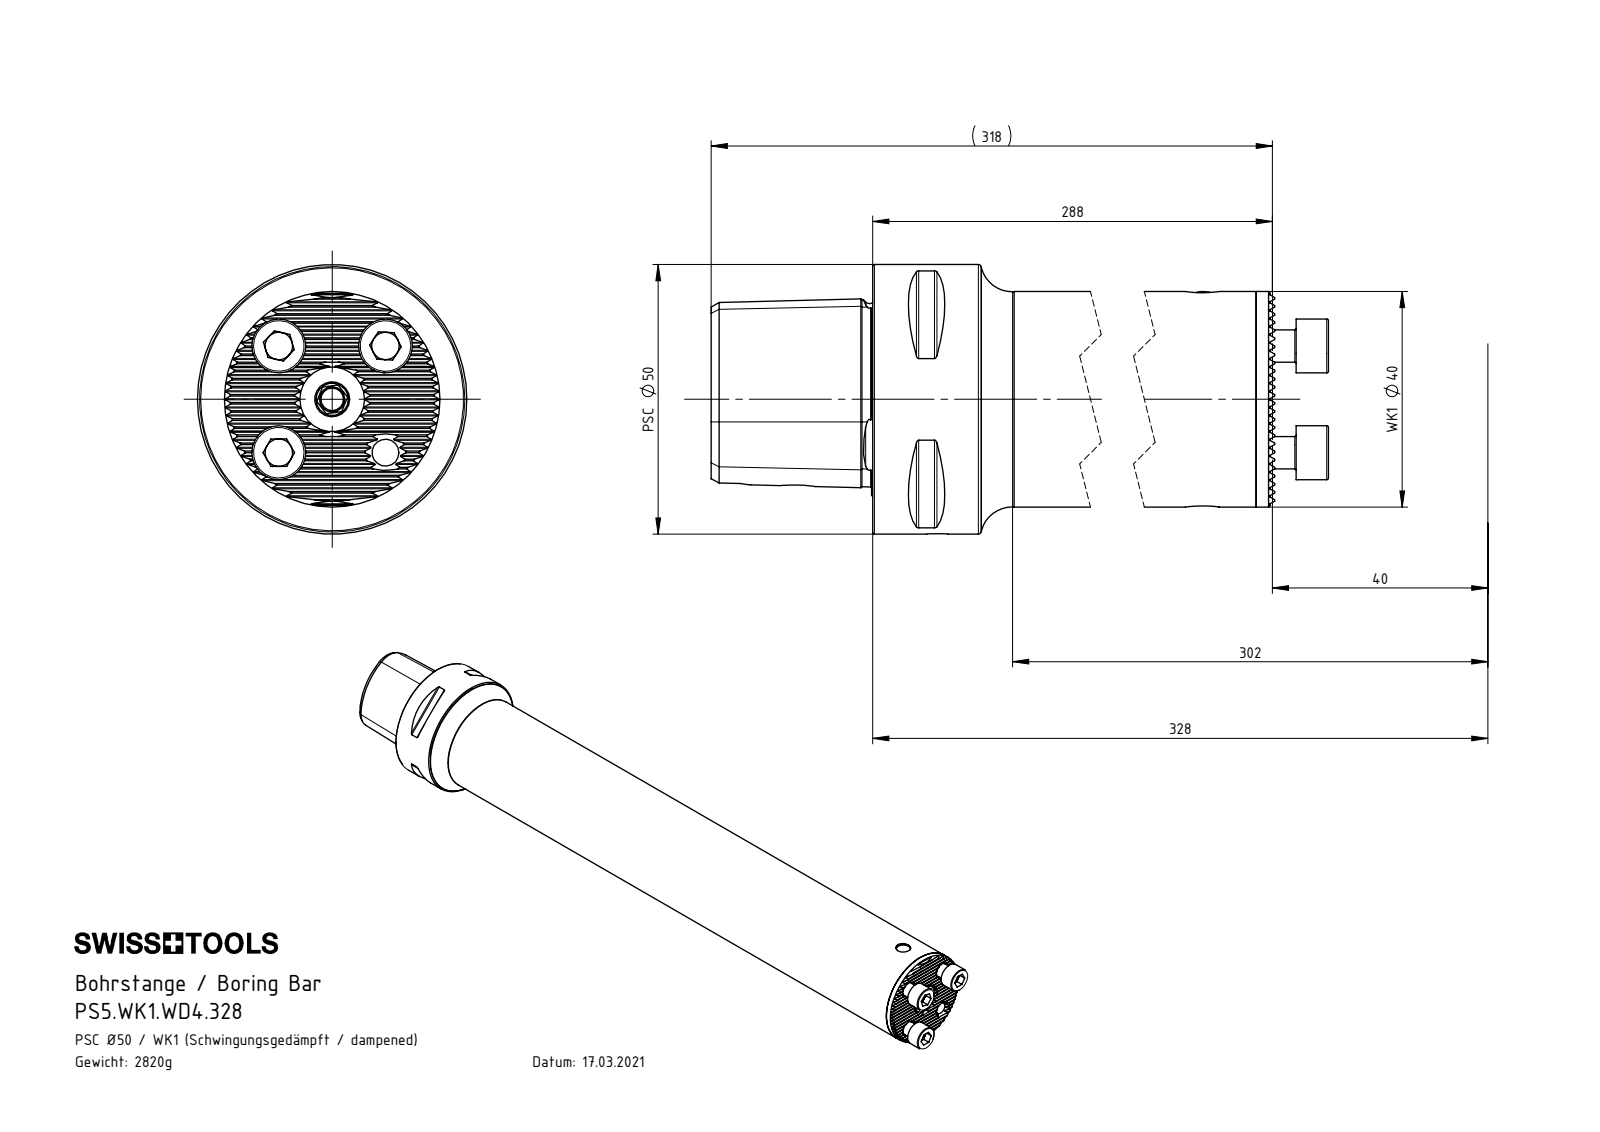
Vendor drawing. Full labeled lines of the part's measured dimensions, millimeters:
Part name (STEP PRODUCT): DIN 3771 - 13x4; WD4-ER1.011.107_A; PS5-WD4.125.285_A_mit Stiftbohrung; DIN 6325_ø6x16-m6_2x6 (+8 more)
STEP written by: SolidWorks 2017 (AUTOMOTIVE_DESIGN)
Units: millimetres
Bodies: 16 solids, 530 faces (266 planar, 120 cylindrical, 144 other)
Overall size (bounding box): 328.4 × 50 × 50
Volume: 364 499 mm³ · Surface area: 108 802 mm²
Round holes (diameter × count): ⌀5 ×4, ⌀6 ×2, ⌀4 ×1, ⌀4.2 ×1, ⌀6.1 ×1, ⌀7 ×1, ⌀7.4 ×1, ⌀8.5 ×1, ⌀12 ×1, ⌀14 ×1, ⌀14.5 ×1, ⌀21 ×1
Round bosses / shafts (diameter × count): ⌀10 ×3, ⌀6 ×3, ⌀50 ×1, ⌀40 ×1, ⌀35 ×1, ⌀34.7 ×1, ⌀34 ×1, ⌀31.8 ×1
Partial cylindrical surfaces — rounded edges, fillets, slot ends (radius × count): R0.12 ×27, R0.5 ×8, R4 ×1
Main face-to-face distances: 6, 118.4, 6.2, 118.2, 112.2, 2.6, 112.4, 119.25, 6.85, 124.4
Hole centre spacings: 14, 19.8, 28, 26, 263, 289
